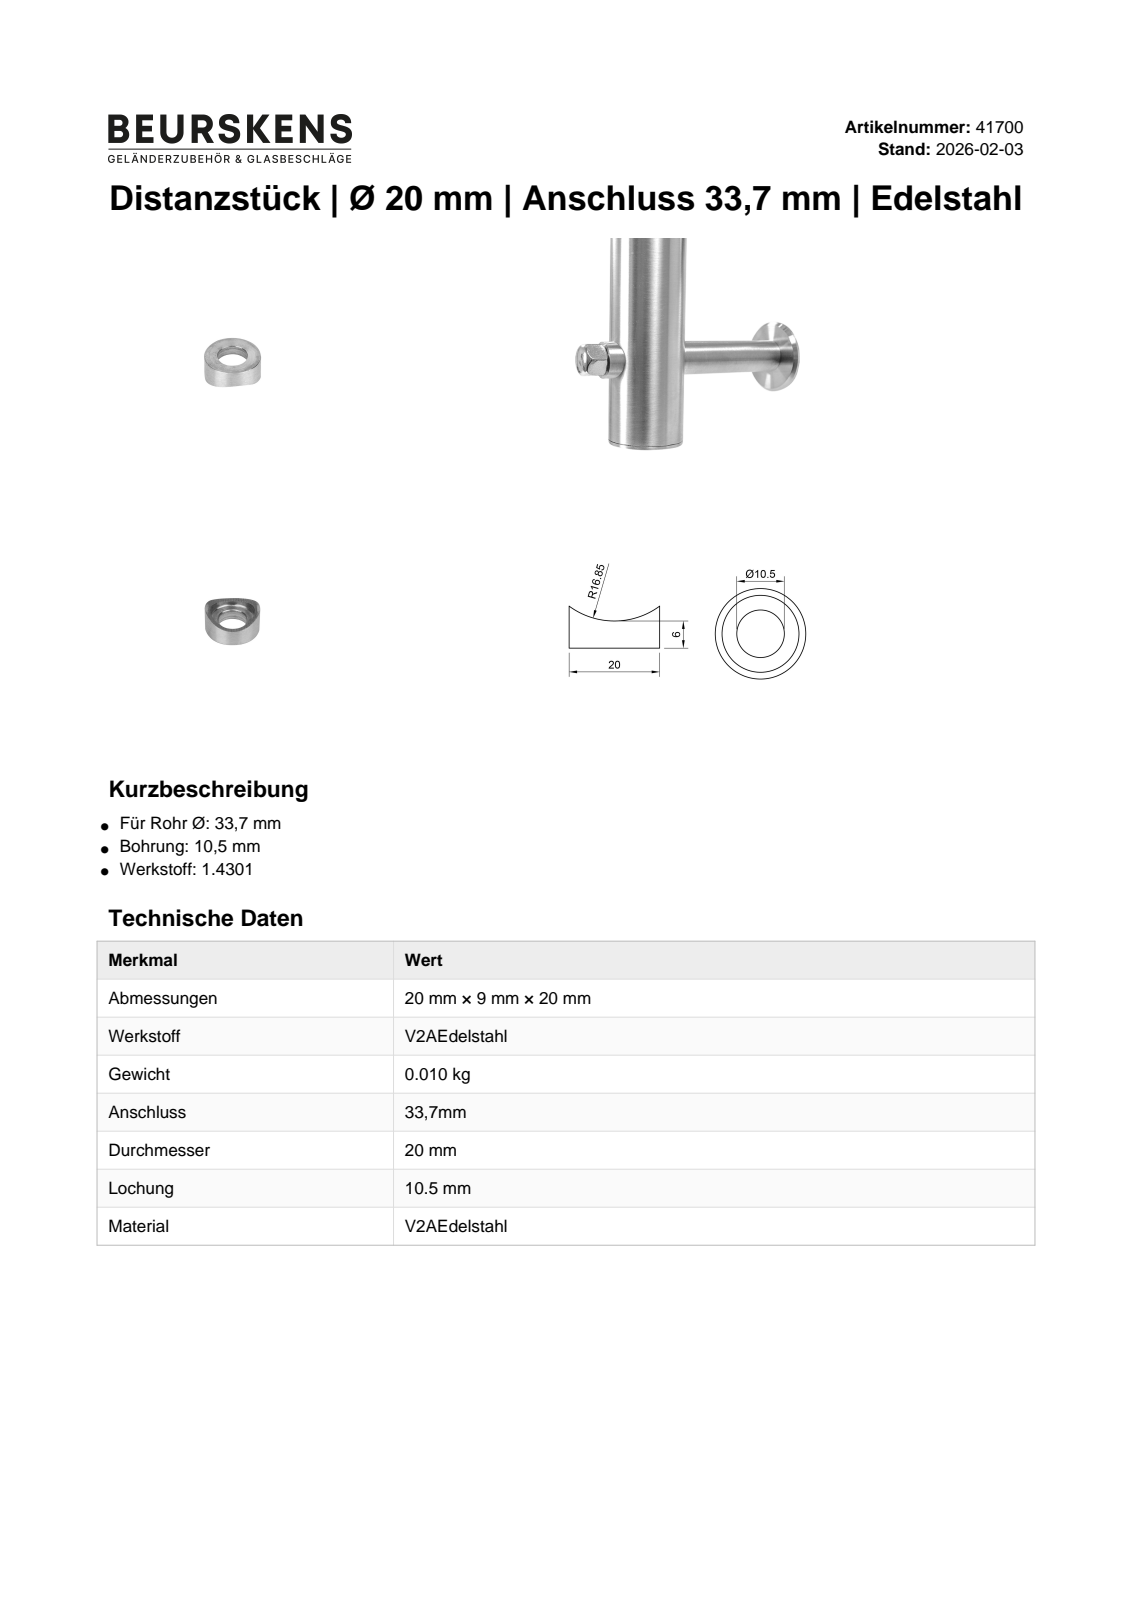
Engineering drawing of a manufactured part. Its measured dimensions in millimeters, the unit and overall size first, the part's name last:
Units: millimetres
Overall size (bounding box): 20 × 20 × 9.29
Round holes (diameter × count): ⌀10.5 ×1
Round bosses / shafts (diameter × count): ⌀20 ×1
Partial cylindrical surfaces — rounded edges, fillets, slot ends (radius × count): R16.85 ×1
Main face-to-face distances: 5.45
Volume: 1 409 mm³ · Surface area: 1 210 mm²
Bodies: 1 solid, 6 faces (2 planar, 3 cylindrical, 1 other)
Part name (STEP PRODUCT): 41700
STEP written by: Autodesk Inventor 2022 (AUTOMOTIVE_DESIGN)
